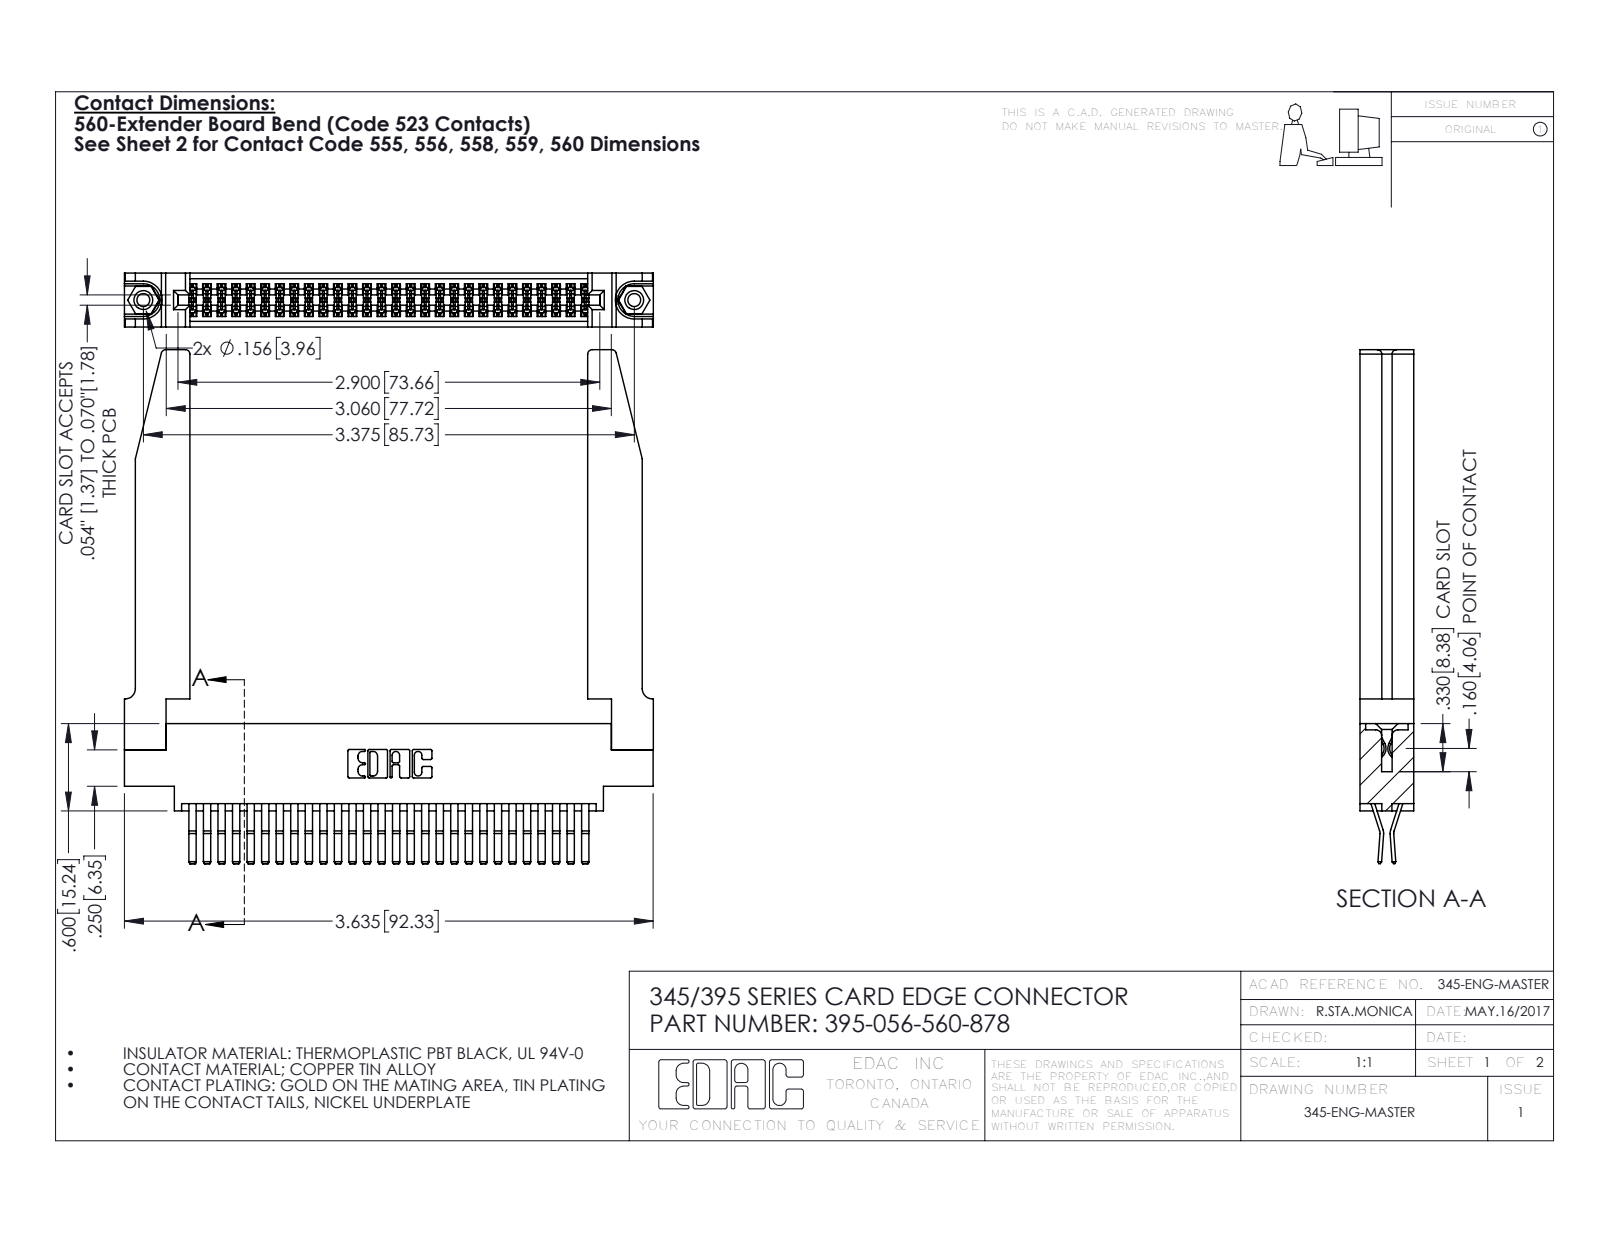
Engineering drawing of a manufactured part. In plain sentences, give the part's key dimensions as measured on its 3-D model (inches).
The part is named "345-292-001_560 Tail; 345-250-001_345-250-001-102; 345 Part_0.170 Offset - 0.156 Dia-TH; 395-056-560-878 (+1 more)". Its 3-D file was written by "SolidWorks 2016 (CONFIG_CONTROL_DESIGN)". It is 61 solids with 3276 faces: 2074 planar, 1150 cylindrical and 52 other. Overall it measures 3.636 by 3.532 by 0.37 inches. Its volume is 1.029 cubic inches and its surface area 32.7 square inches. Round holes: 2 of diameter 0.089, 2 of diameter 0.125, 2 of diameter 0.156, 1 of diameter 0.064. Round bosses or shafts: 2 of diameter 0.155. Partial cylindrical surfaces (rounded edges, fillets, slot ends): 111 of radius 0.006, 22 of radius 0.01, 8 of radius 0.03, 6 of radius 0.007, 6 of radius 0.031, 3 of radius 0.026, 2 of radius 0.01, 2 of radius 0.014. The main face-to-face distances are 0.37, 0.072, 0.298, 0.025, 0.098, 0.272, 0.2, 0.225, 0.148, 0.15. The hole center spacings are 0.27, 3.14, 3.375.
